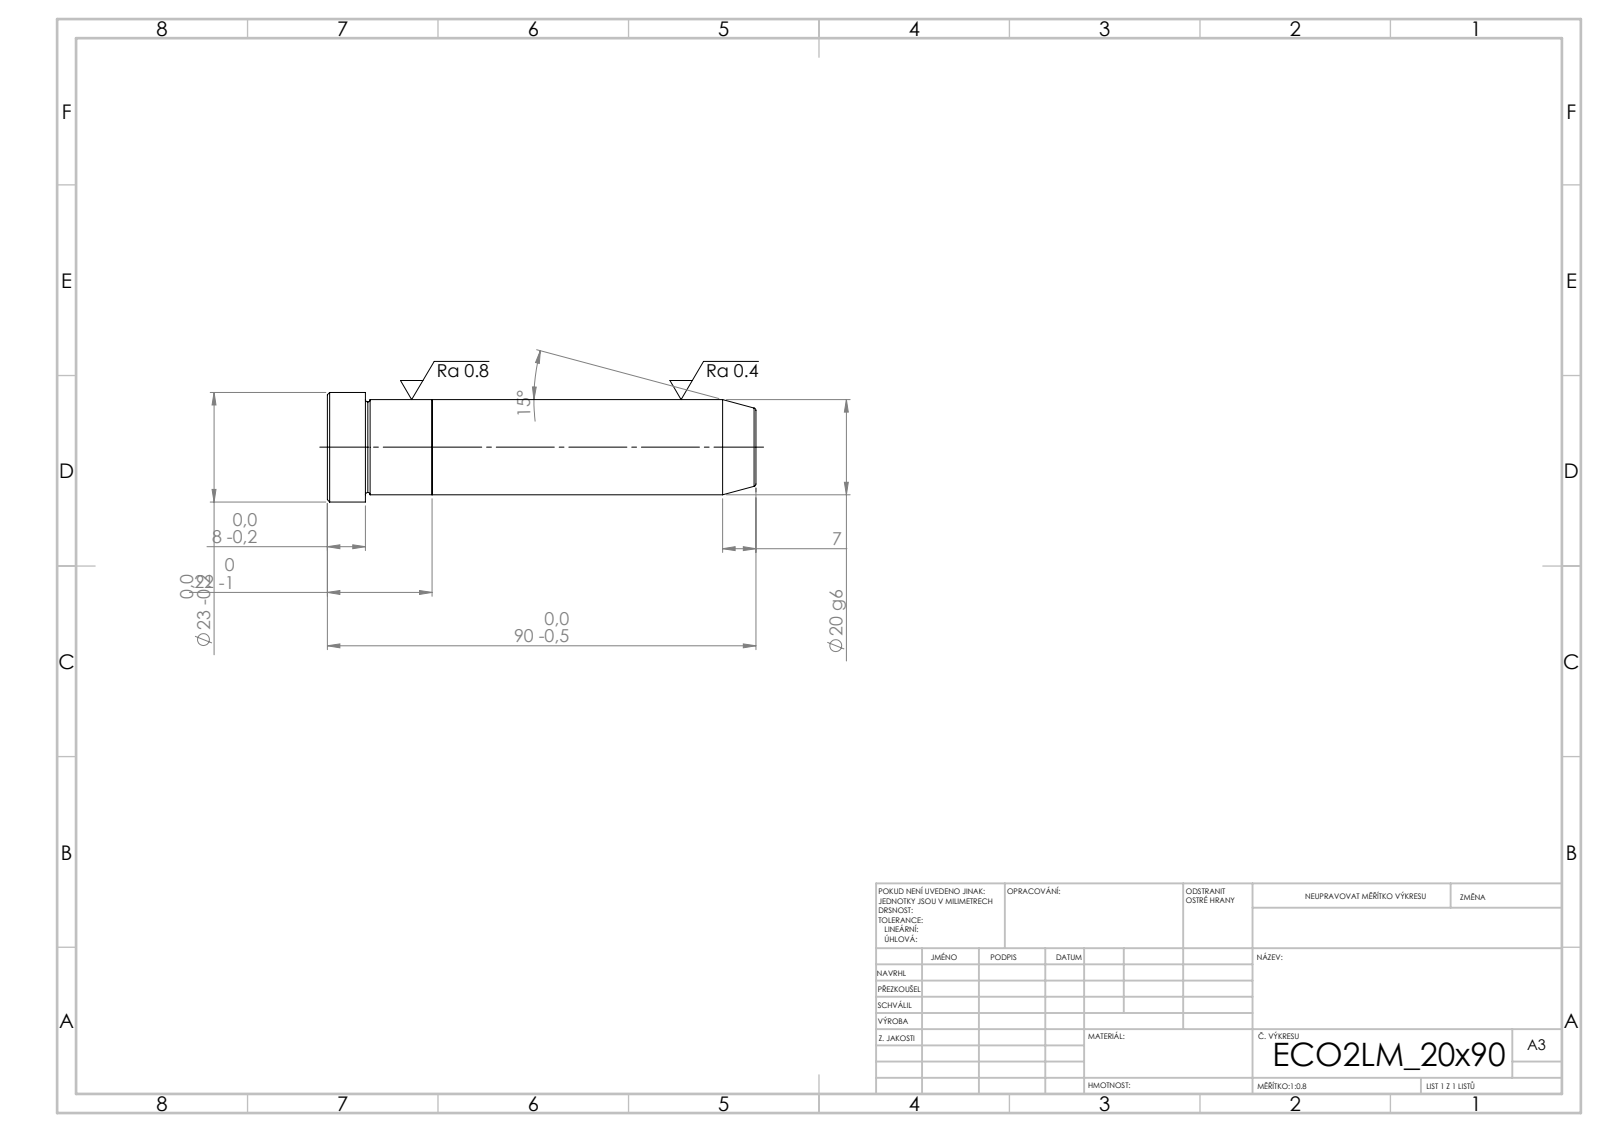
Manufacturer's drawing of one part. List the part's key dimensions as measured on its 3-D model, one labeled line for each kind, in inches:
STEP written by: SolidWorks 2019 (CONFIG_CONTROL_DESIGN)
Units: inches
Bodies: 2 solids, 21 faces (5 planar, 6 cylindrical, 10 other)
Overall size (bounding box): 3.543 × 0.906 × 0.906
Volume: 1.749 in³ · Surface area: 10.94 in²
Round bosses / shafts (diameter × count): ⌀0.906 ×1, ⌀0.787 ×1
Main face-to-face distances: 0.866, 2.677, 3.543, 3.228, 0.551, 0.315
